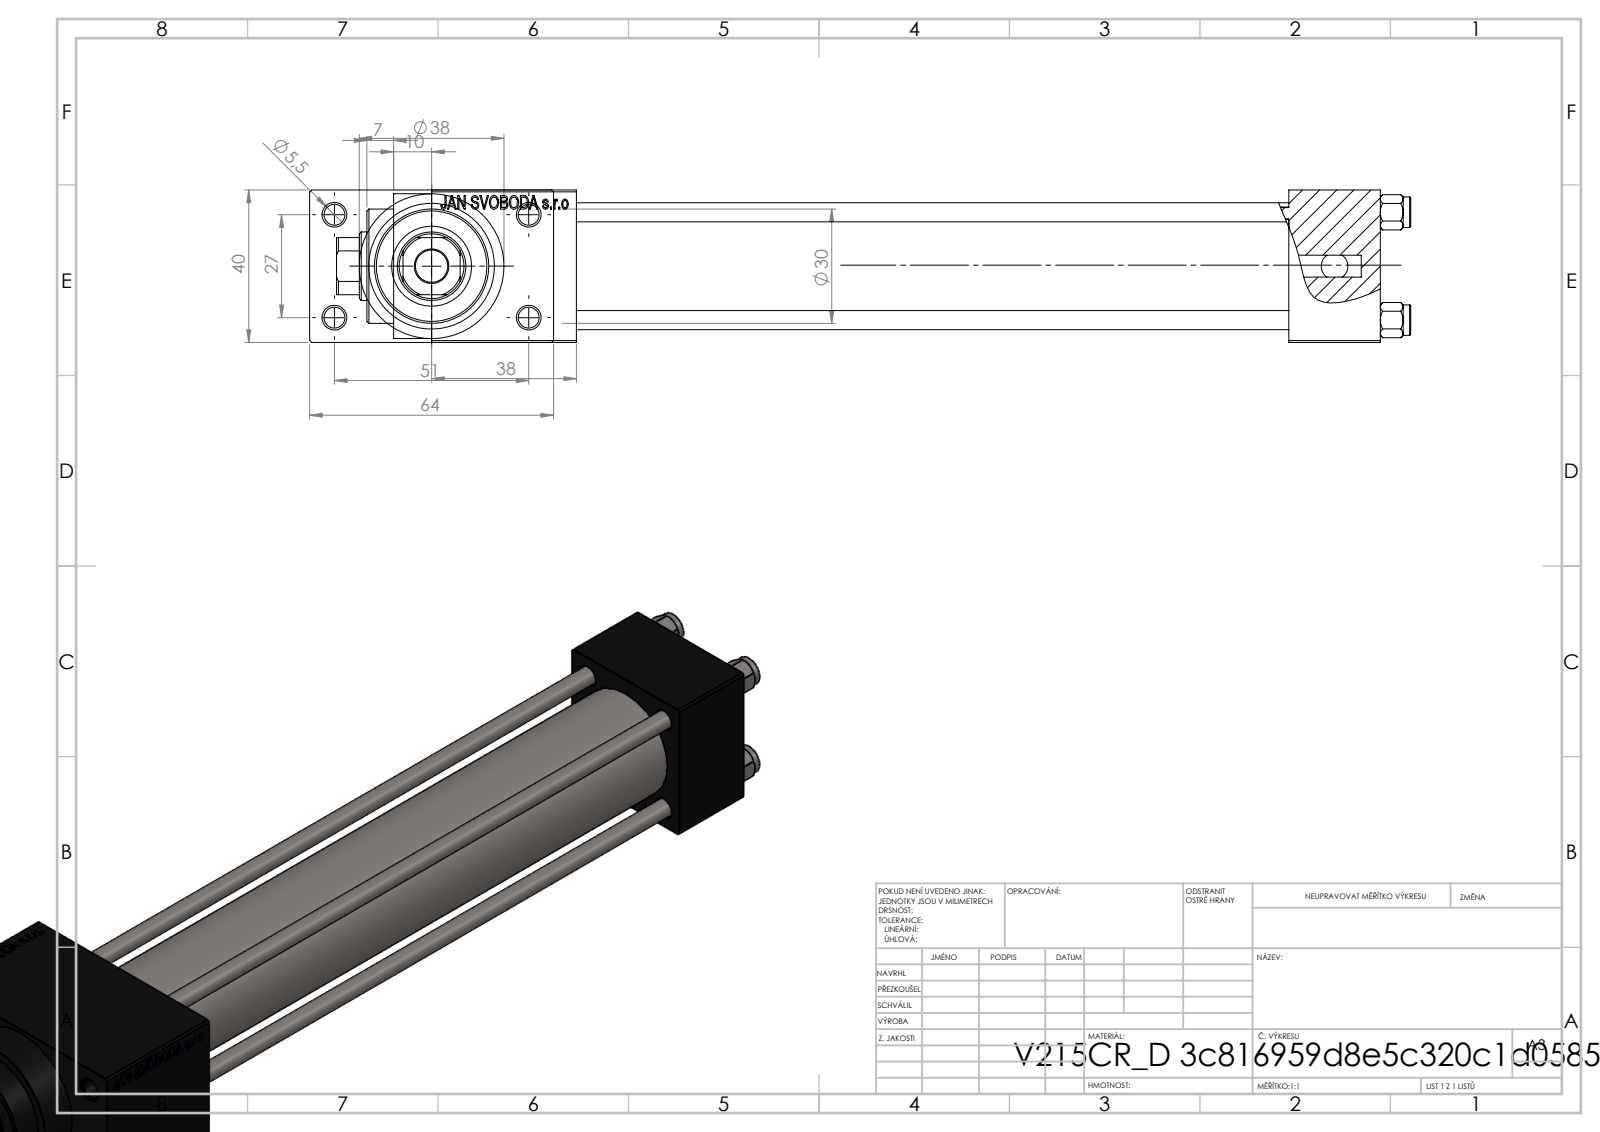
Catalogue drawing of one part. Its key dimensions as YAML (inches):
part_name: "NUT_M5_D; V215_VC_A; V215CR_D_Body; V215CR_VCP_D (+1 more)"
step_written_by: "SolidWorks 2019 (CONFIG_CONTROL_DESIGN)"
units: inches
bodies: {solids: 11, faces: 1101, planar: 495, cylindrical: 86, other: 520}
overall_size: [11.102, 2.52, 1.575]
volume: 16.03
surface_area: 164.3
round_holes:
  - {diameter: 0.197, count: 4}
  - {diameter: 0.217, count: 4}
  - {diameter: 0.787, count: 3}
  - {diameter: 0.276, count: 2}
  - {diameter: 0.518, count: 2}
  - {diameter: 0.335, count: 1}
  - {diameter: 0.709, count: 1}
  - {diameter: 0.827, count: 1}
  - {diameter: 0.984, count: 1}
  - {diameter: 1.181, count: 1}
round_bosses_or_shafts:
  - {diameter: 0.315, count: 4}
  - {diameter: 1.496, count: 1}
  - {diameter: 1.22, count: 1}
partial_cylinders:
  - {radius: 0.335, count: 1}
face_to_face_distances: [1.575, 0.472, 7.362, 0.945, 8.307, 2.047, 1.496, 9.803, 8.858, 2.52]
hole_center_spacings: [0.448, 0.788, 1.114, 1.136, 1.177, 1.561, 1.903, 1.063]
